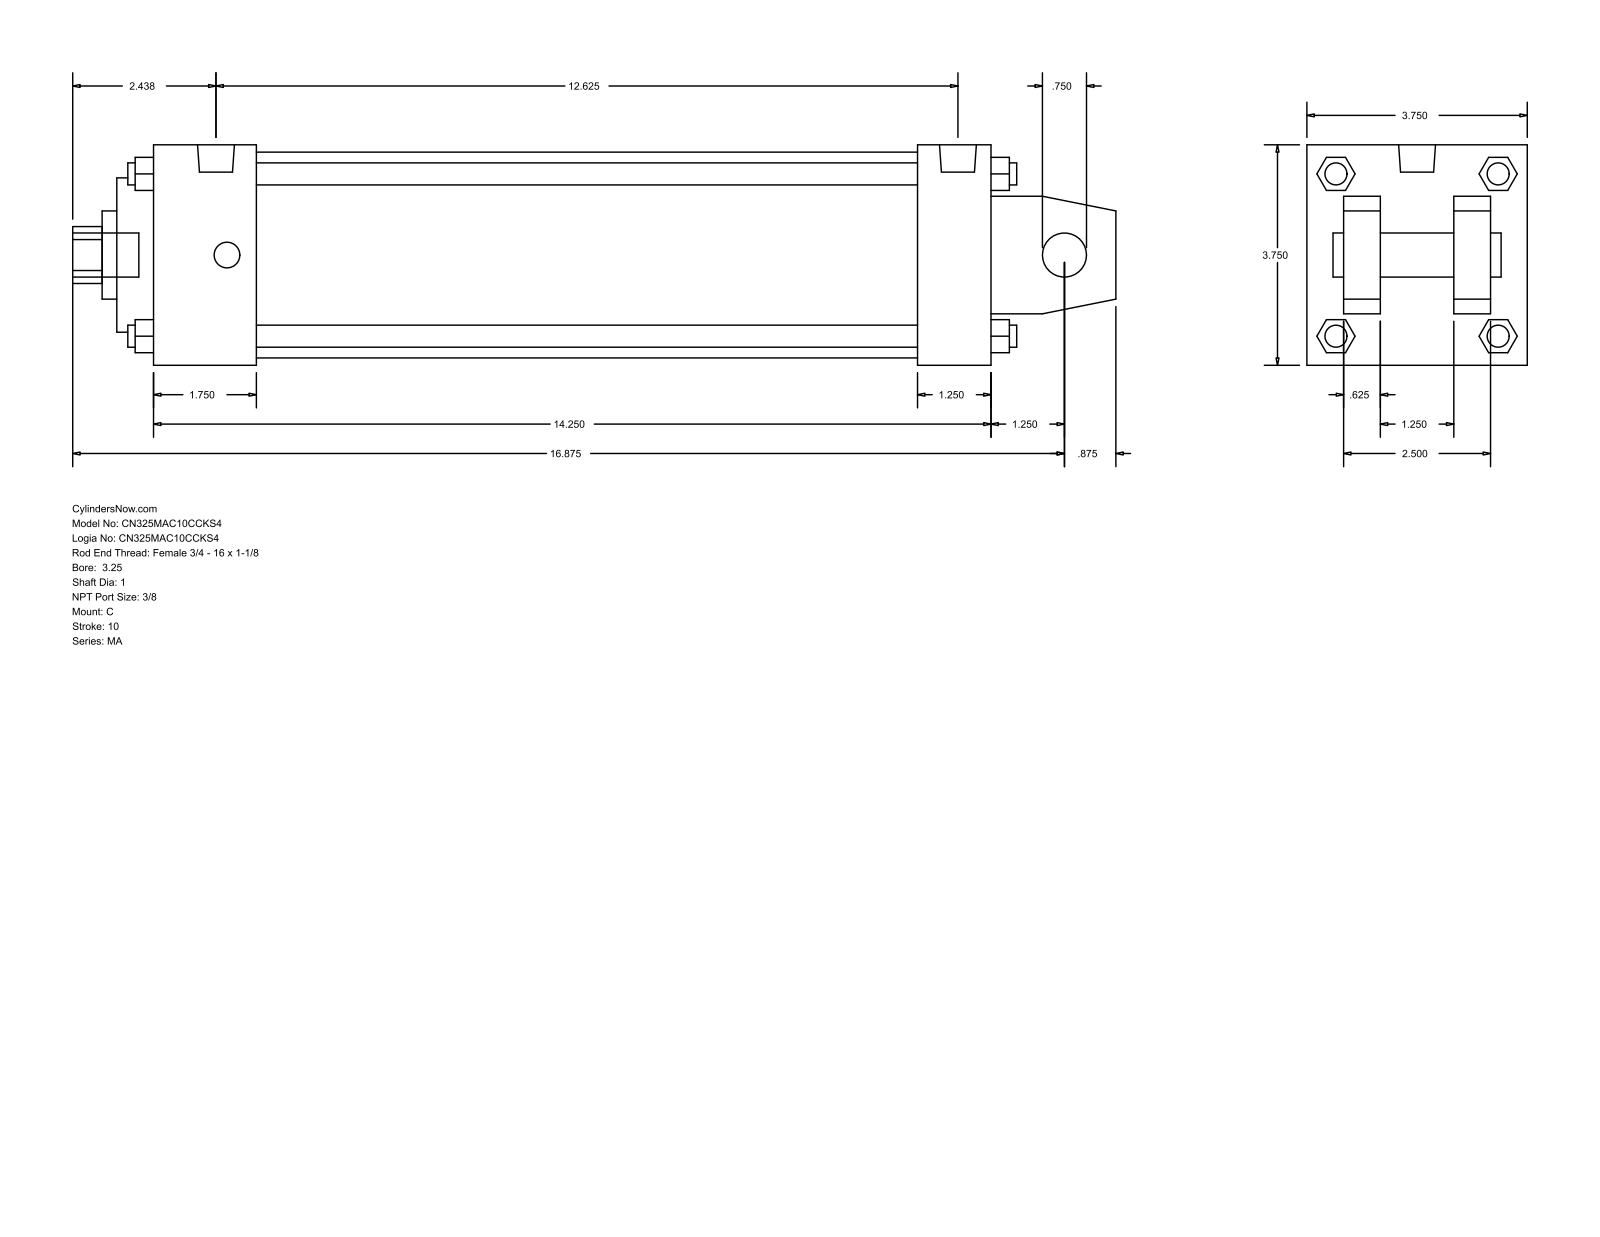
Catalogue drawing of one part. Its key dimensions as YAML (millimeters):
part_name: "MA_C__0325_1"
step_written_by: "GSSL Pune (CONFIG_CONTROL_DESIGN)"
units: millimeters
bodies: {solids: 0, faces: 141, planar: 109, cylindrical: 32, other: 0}
overall_size: [450.85, 95.25, 95.25]
round_holes:
  - {diameter: 19.05, count: 1}
  - {diameter: 25.4, count: 1}
  - {diameter: 38.1, count: 1}
  - {diameter: 66.67, count: 1}
  - {diameter: 88.9, count: 1}
round_bosses_or_shafts:
  - {diameter: 11.11, count: 4}
  - {diameter: 9.53, count: 4}
  - {diameter: 15.93, count: 2}
  - {diameter: 19.05, count: 1}
partial_cylinders:
  - {radius: 12.29, count: 1}
face_to_face_distances: [95.24, 15.87, 63.5, 361.96, 31.76, 31.74, 79.37, 47.63, 330.2, 44.46]
